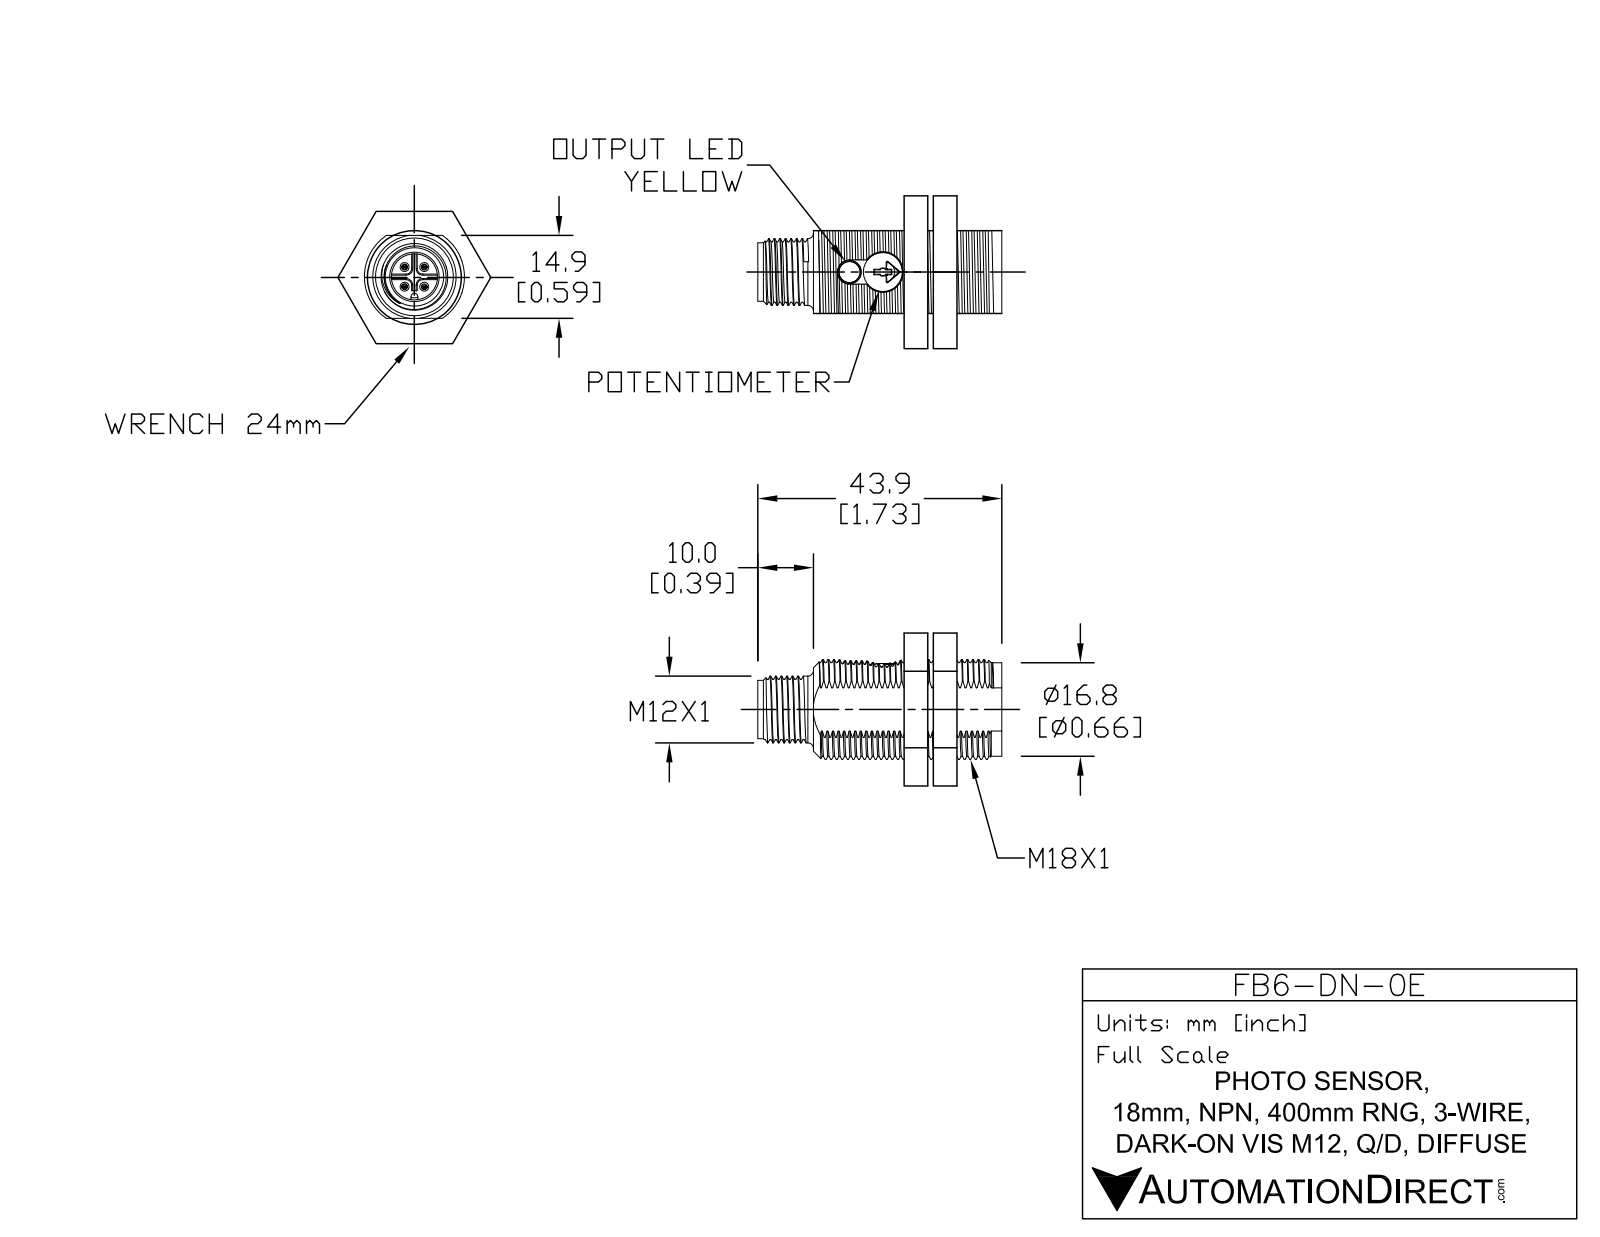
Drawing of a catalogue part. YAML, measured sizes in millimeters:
part_name: "FB6-DN-0E"
step_written_by: "SolidWorks 2011 (AUTOMOTIVE_DESIGN)"
units: millimeters
bodies: {solids: 7, faces: 231, planar: 134, cylindrical: 33, other: 64}
overall_size: [43.9, 27.69, 24.57]
volume: 10307
surface_area: 5166
round_holes:
  - {diameter: 2.36, count: 1}
  - {diameter: 4.26, count: 1}
  - {diameter: 7.25, count: 1}
  - {diameter: 8.4, count: 1}
round_bosses_or_shafts:
  - {diameter: 1, count: 4}
  - {diameter: 12, count: 1}
  - {diameter: 10.4, count: 1}
partial_cylinders:
  - {radius: 6.46, count: 2}
  - {radius: 7.46, count: 2}
  - {radius: 0.5, count: 1}
  - {radius: 0.65, count: 1}
  - {radius: 8.4, count: 1}
  - {radius: 8.5, count: 1}
  - {radius: 9, count: 1}
face_to_face_distances: [8, 4.5, 24, 15, 1, 12.5, 3.5, 12.9, 13.9, 4.9]
hole_center_spacings: [6.61]
